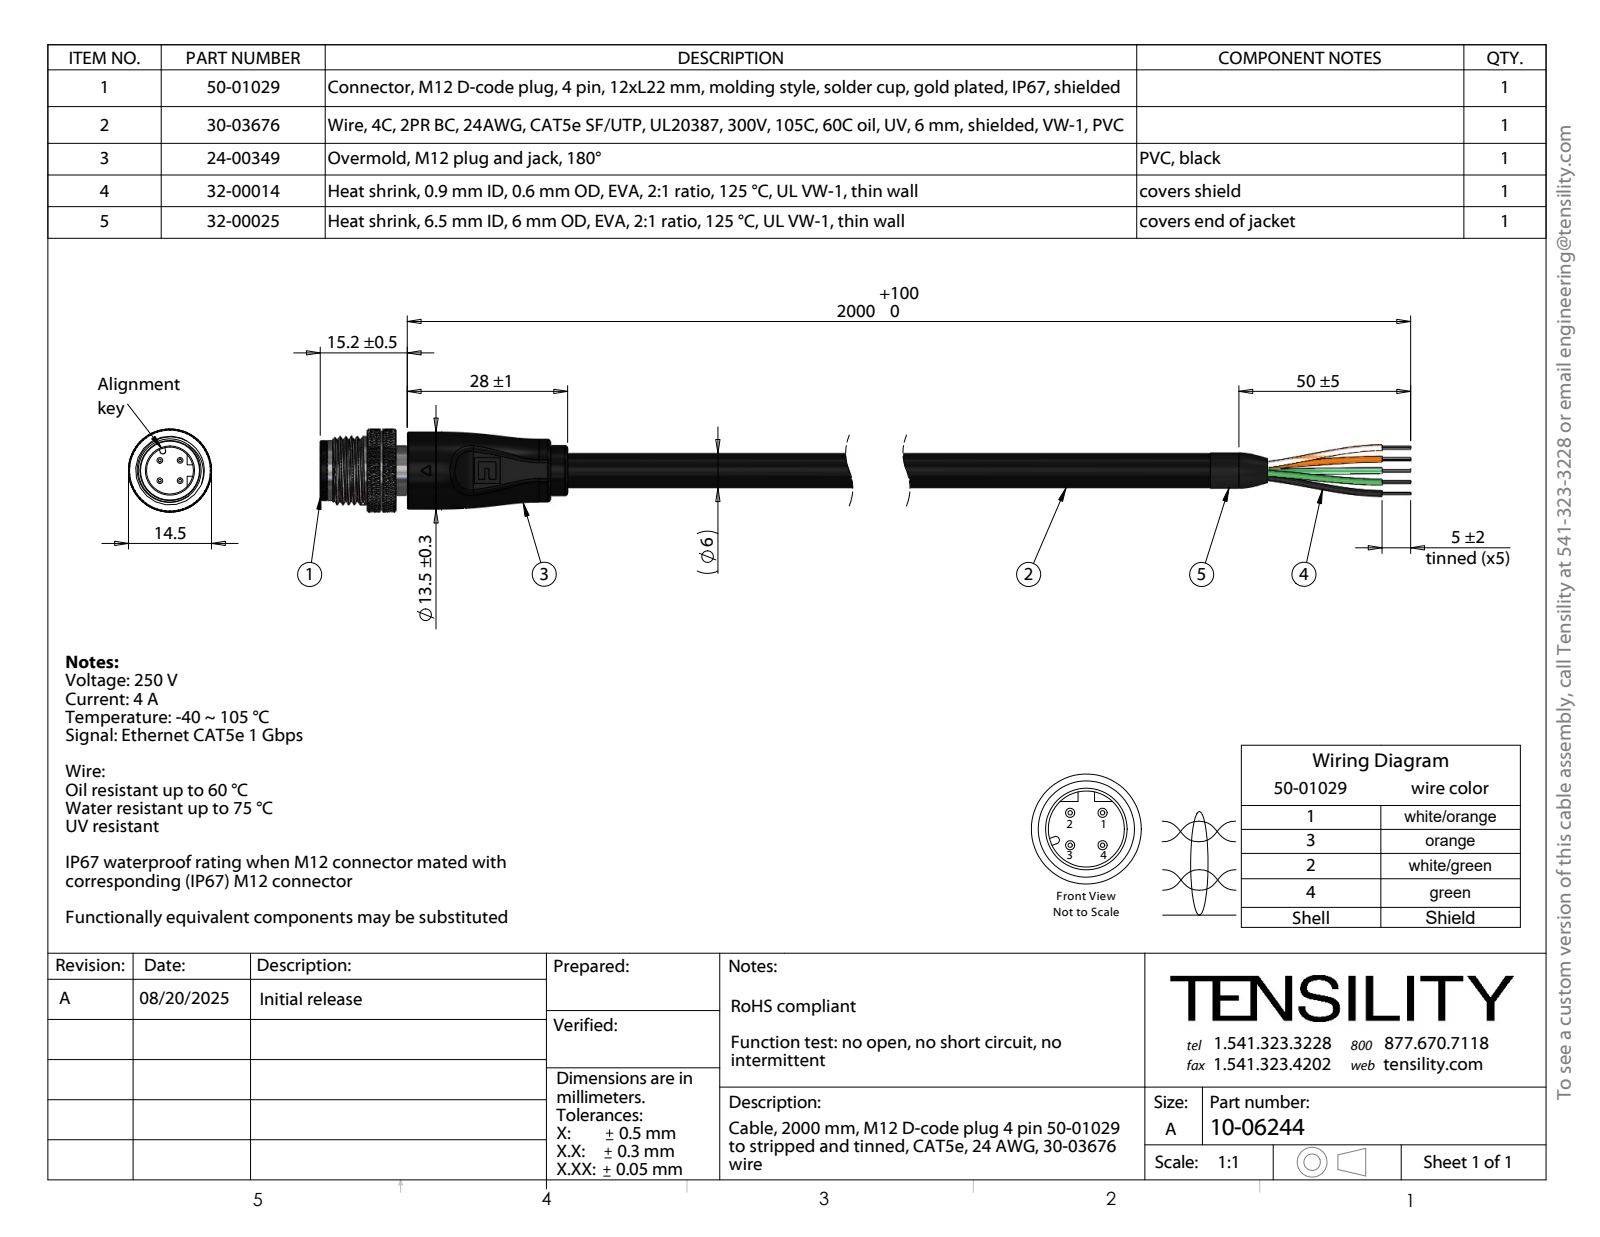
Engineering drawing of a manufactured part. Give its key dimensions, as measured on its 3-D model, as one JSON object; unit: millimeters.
{"part_name": "30-03676_s + t; 24-00349_Mexico; 50-01029_默认; 50-01029-04_默认 (+4 more)", "step_written_by": "SolidWorks 2025 (CONFIG_CONTROL_DESIGN)", "units": "millimeters", "bodies": {"solids": 86, "faces": 2792, "planar": 263, "cylindrical": 823, "other": 1706}, "overall_size": [223.2, 14.5, 14.5], "volume_mm3": 9287, "surface_area_mm2": 26453, "round_holes": [[0.2, 28], [1, 4], [1.05, 4], [3.16, 1], [3.21, 1], [3.36, 1], [8, 1], [8.2, 1], [8.8, 1], [9.5, 1]], "round_bosses_or_shafts": [[0.2, 35], [1.4, 4], [14.5, 1], [13.9, 1], [13.5, 1], [12, 1], [11, 1], [10.5, 1]], "partial_cylinders_radius": [[0.5, 2], [1.5, 2], [1.96, 2], [5, 1], [5.58, 1], [6.75, 1]], "face_to_face_distances": [180, 7, 2, 178, 5, 28, 30, 150, 10.8, 3.8], "hole_center_spacings": [1.91, 2.09, 1.06, 0.35, 0.89, 1.08, 1.24, 1.71]}
